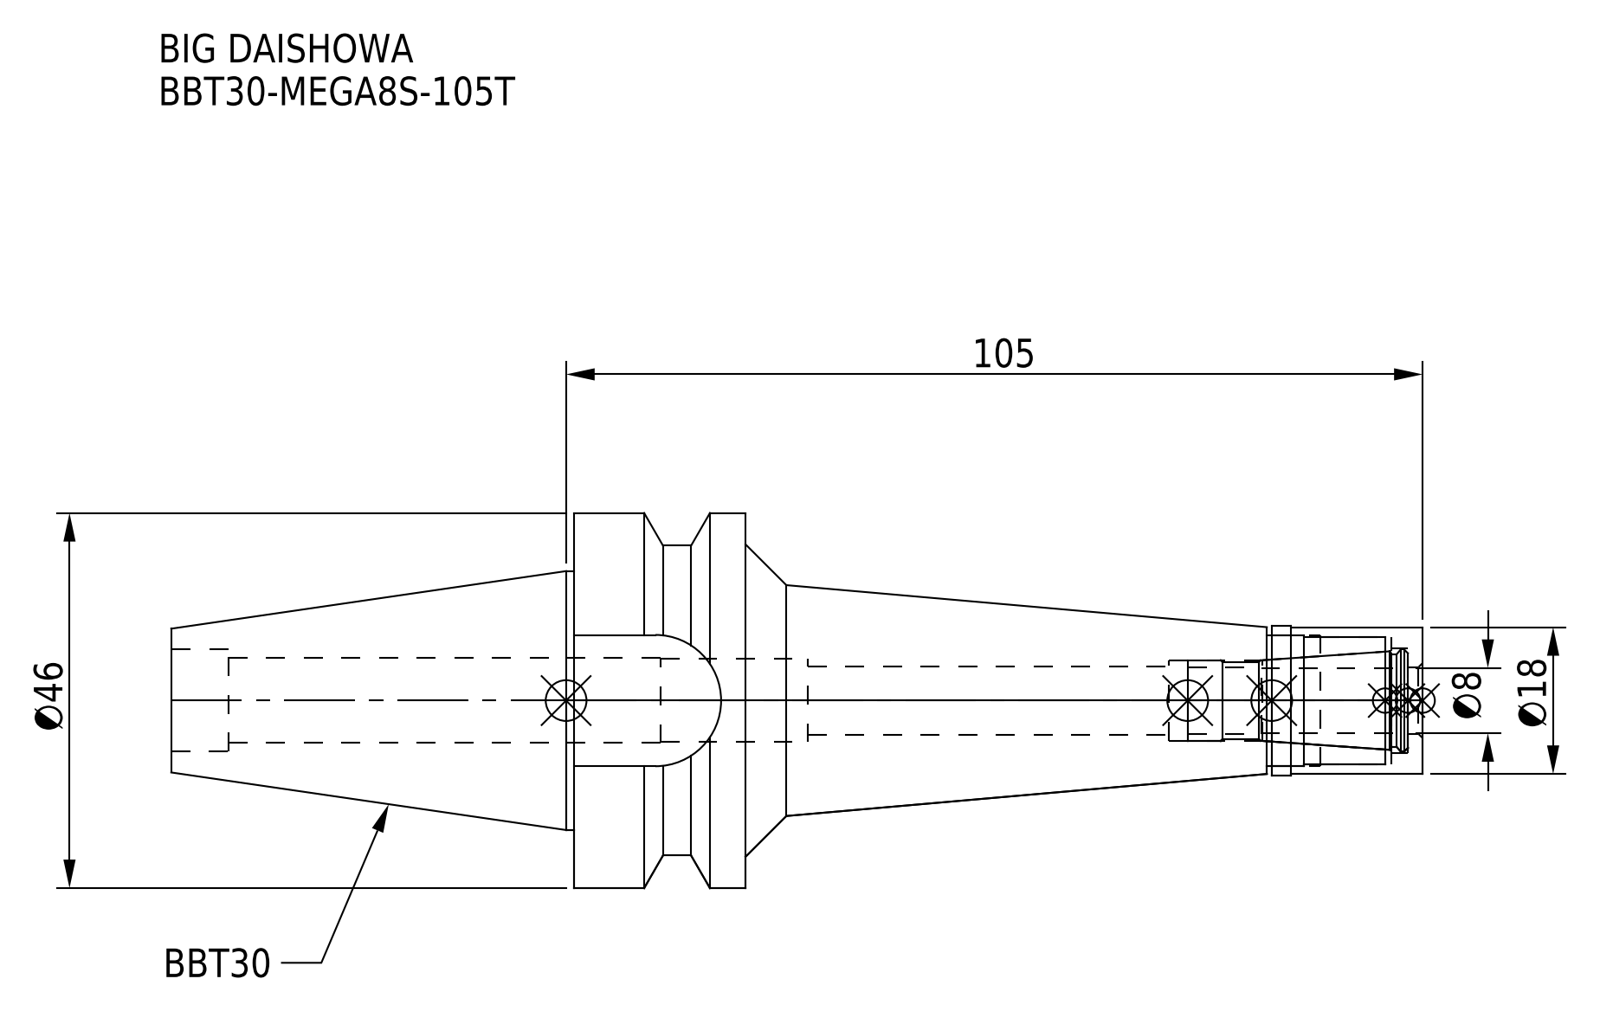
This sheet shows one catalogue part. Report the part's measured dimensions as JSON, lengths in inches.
{"part_name": "BBT30-MEGA8S-105T-FreeParts; BBT30MS08105T-080_ASM.stp; BBT30-MEGA8S-105T.stp; BBT30-MEGA8S-105T (+3 more)", "step_written_by": "SolidWorks 2019 (CONFIG_CONTROL_DESIGN)", "units": "inches", "bodies": {"solids": 2, "faces": 74, "planar": 22, "cylindrical": 38, "other": 14}, "overall_size": [6.039, 1.811, 1.811], "volume_in3": 4.647, "surface_area_in2": 33.93, "round_holes": [[0.323, 1], [0.331, 1], [0.39, 1], [0.402, 1], [0.409, 1], [0.492, 1], [0.508, 1], [0.614, 1], [0.634, 1]], "round_bosses_or_shafts": [[1.811, 1], [1.25, 1], [0.72, 1], [0.709, 1]], "partial_cylinders_radius": [[0.317, 1], [0.748, 1]], "face_to_face_distances": [0.827, 1.283, 3.268, 4.094, 6.039, 2.772, 1.945, 0.634, 0.181, 3.087]}
